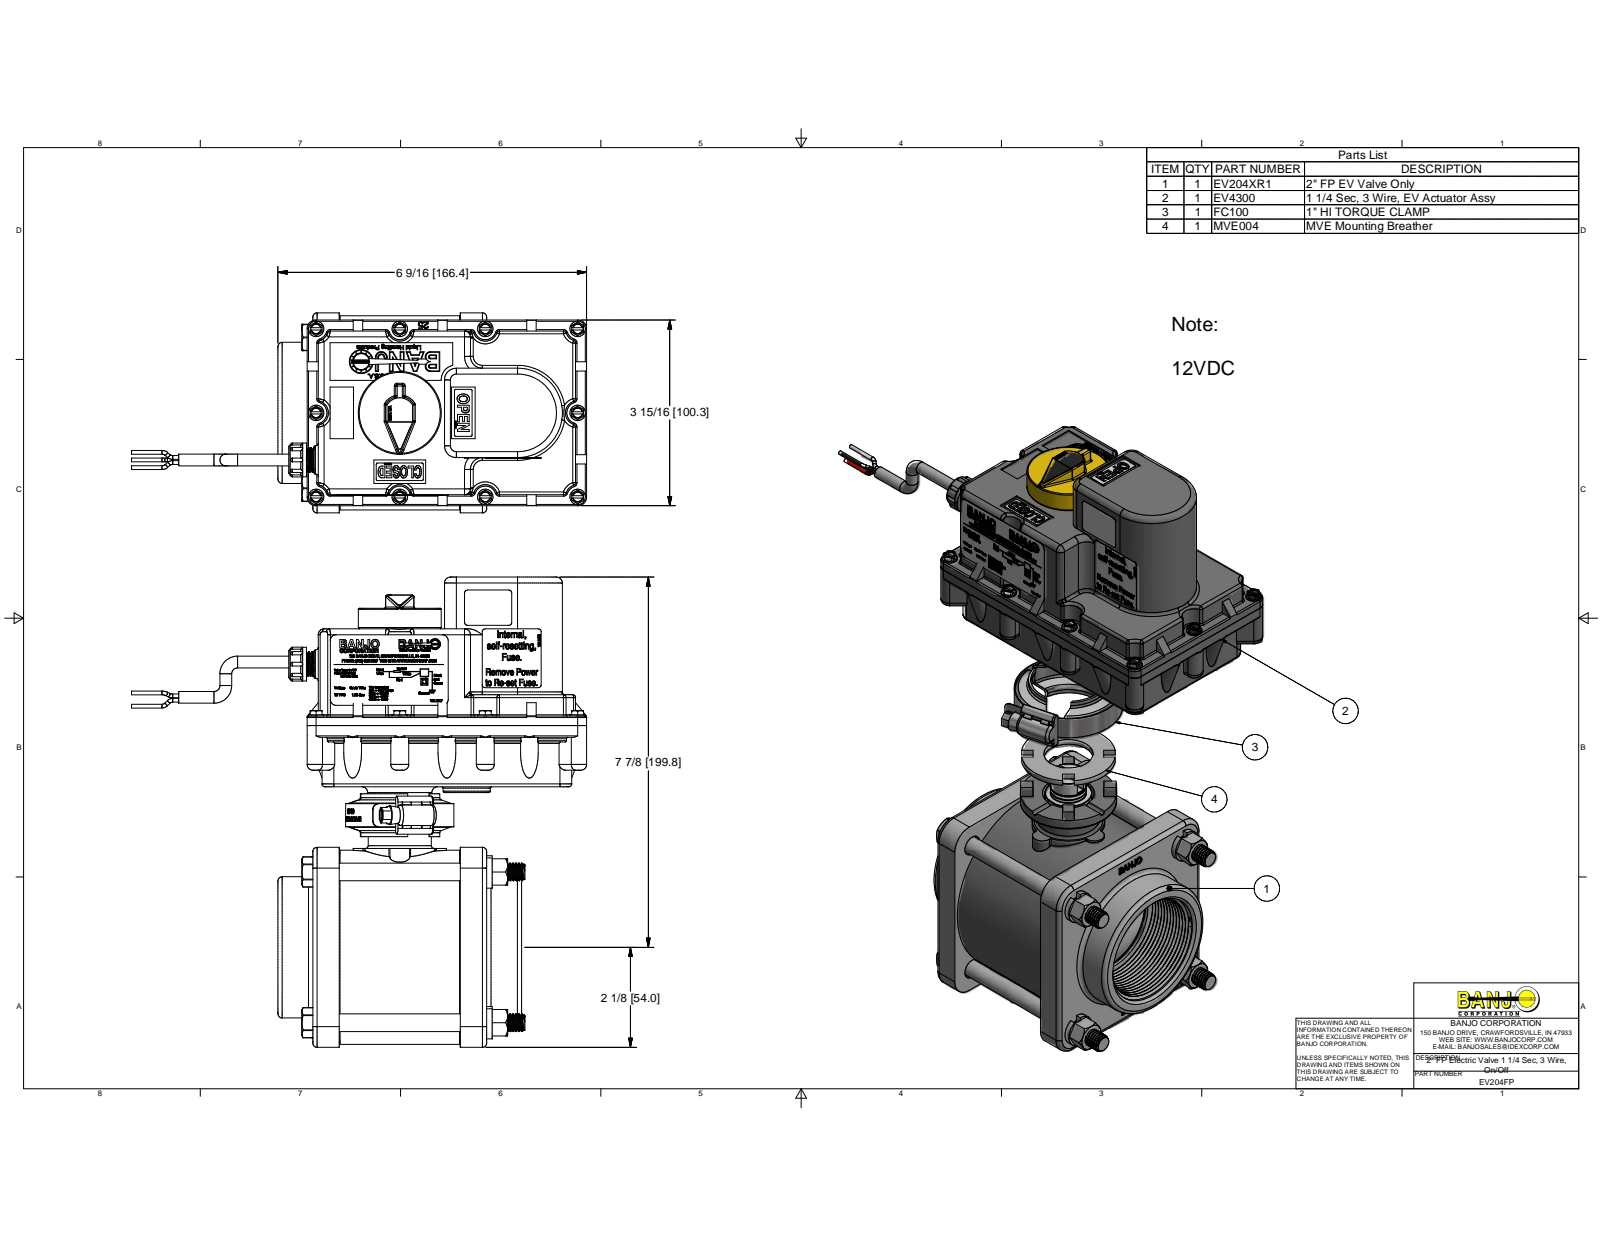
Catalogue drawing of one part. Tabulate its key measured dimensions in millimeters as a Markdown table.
| quantity | value |
| --- | --- |
| part name | MEV25254AX; MEV25254A; VE25255SSH; MEV25151SS (+8 more) |
| STEP written by | Autodesk Inventor 2016 (AUTOMOTIVE_DESIGN) |
| units | millimeters |
| bodies | 78 solids, 11676 faces (5487 planar, 1557 cylindrical, 4632 other) |
| overall size | 253.81 × 245.26 × 107.95 |
| volume | 1 303 000 mm³ |
| surface area | 511 415 mm² |
| round holes (diameter × count) | 2.79 × 10, 4.06 × 10, 5.08 × 10, 1.52 × 8, 3.05 × 6, 3.81 × 6, 0.38 × 4, 2.26 × 4, 3.3 × 4, 3.45 × 4, 4.44 × 4, 4.47 × 4 |
| round bosses / shafts (diameter × count) | 8.24 × 60, 8.33 × 10, 3.51 × 10, 6.35 × 9, 2.03 × 9, 2.62 × 8, 8 × 6, 7.62 × 6 |
| partial cylindrical surfaces (radius × count) | 0.76 × 125, 0.51 × 62, 1.52 × 47, 3.17 × 32, 1.59 × 26, 8 × 24, 12.7 × 24, 9.91 × 16 |
| main face-to-face distances | 33.02, 3.18, 5.08, 20.07, 27.94, 1.9, 6.98, 3.17, 21.59, 20.32 |
| hole center spacings | 42.68, 52.27, 60.36, 45.34, 2.77, 8.84, 12.5, 30.18 |
